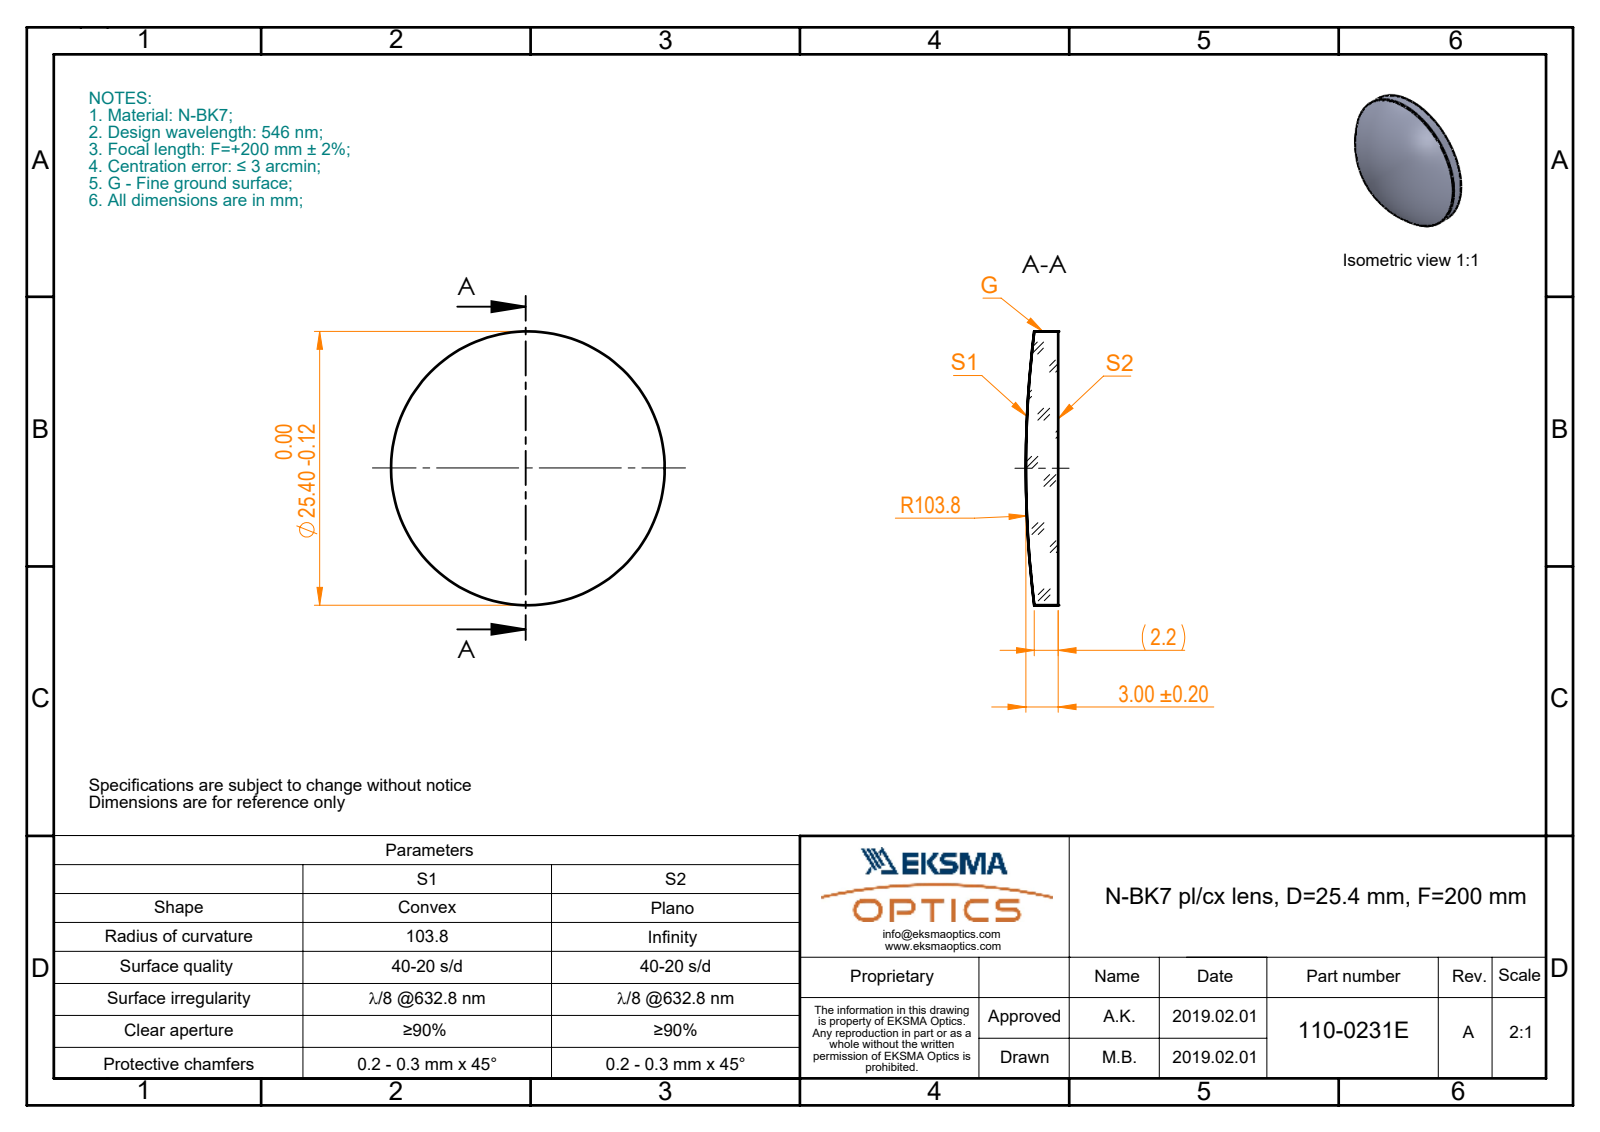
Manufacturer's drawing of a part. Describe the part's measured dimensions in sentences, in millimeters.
The part is named "110-0231E BK7 pl-cx 25.4 F200". Its 3-D file was written by "SolidWorks 2017 (CONFIG_CONTROL_DESIGN)". It is 1 solid with 5 faces: 1 planar, 2 cylindrical and 2 other. Overall it measures 25.4 by 25.4 by 3 millimeters. Its volume is 1 323 cubic millimeters and its surface area 1 192 square millimeters. Round bosses or shafts: 1 of diameter 25.4.
